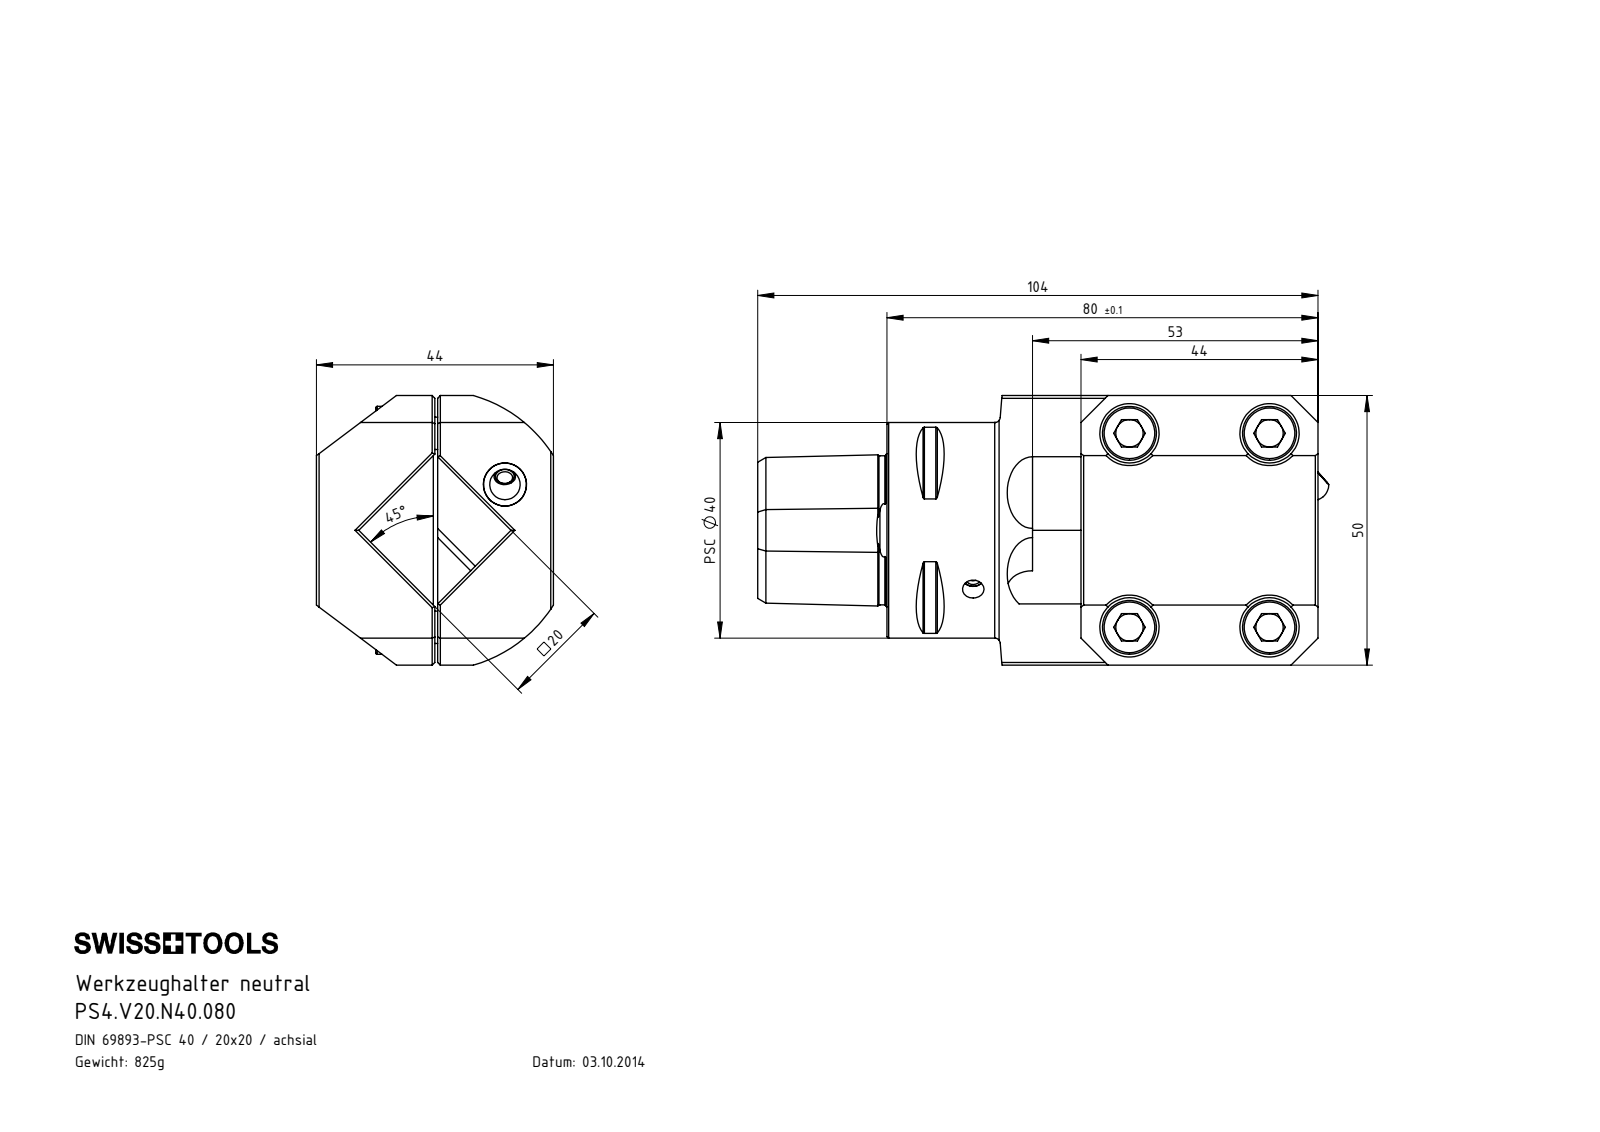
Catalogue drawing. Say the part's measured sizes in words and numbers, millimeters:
The part is named "KVT_MB_600_040; PS4-Vxx.X40.xxx_A_HA4-V20.N40.080; PS4.Vxx.X40.xxx; KU1-U08.001.007_2 (+4 more)". Its 3-D file was written by "SolidWorks 2017 (AUTOMOTIVE_DESIGN)". It is 10 solids with 295 faces: 139 planar, 54 cylindrical and 102 other. Overall it measures 106 by 50 by 44 millimeters. Its volume is 105 198 cubic millimeters and its surface area 32 076 square millimeters. Round holes: 5 of diameter 5, 4 of diameter 6.6, 4 of diameter 11, 2 of diameter 4, 1 of diameter 2.5, 1 of diameter 2.9, 1 of diameter 3, 1 of diameter 4.2, 1 of diameter 4.6, 1 of diameter 8, 1 of diameter 8.5, 1 of diameter 12.5. Round bosses or shafts: 4 of diameter 10, 4 of diameter 6, 1 of diameter 40, 1 of diameter 4. Partial cylindrical surfaces (rounded edges, fillets, slot ends): 8 of radius 0.3, 2 of radius 4.7, 1 of radius 0.8, 1 of radius 3, 1 of radius 26. The main face-to-face distances are 20, 44, 22, 21.5, 22.5, 60, 0.5, 16, 50, 11. The hole center spacings are 26, 36, 37.59, 44.41, 59.3, 61.68, 84.44, 15.53.
